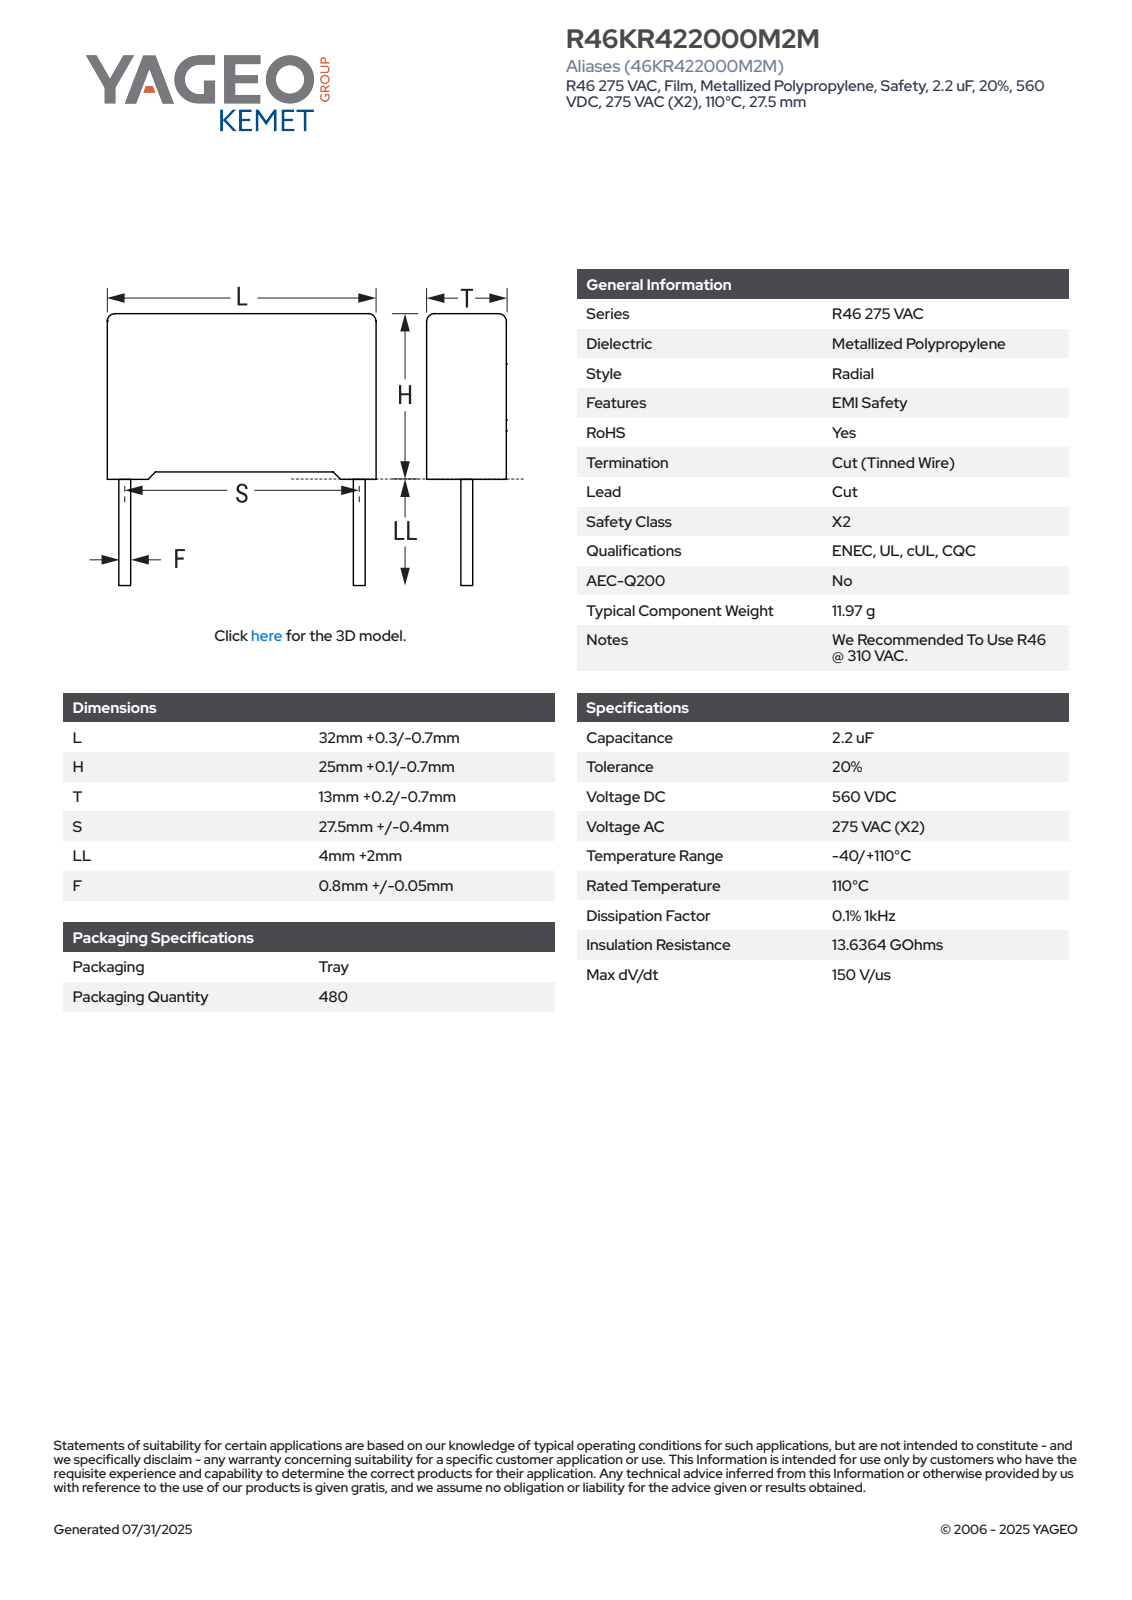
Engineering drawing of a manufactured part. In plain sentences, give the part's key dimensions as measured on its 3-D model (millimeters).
The part is named "CFR_RB2_32X25X13_L32.3H25.1T13.2S27.5LL6F0.85". Its 3-D file was written by "SolidWorks 2021 (AUTOMOTIVE_DESIGN)". It is 4 solids with 85 faces: 77 planar, 8 cylindrical and 0 other. Overall it measures 32.3 by 31.1 by 13.21 millimeters. Its volume is 10 382 cubic millimeters and its surface area 3 219 square millimeters. Round bosses or shafts: 2 of diameter 0.85. Partial cylindrical surfaces (rounded edges, fillets, slot ends): 4 of radius 0.5. The main face-to-face distances are 13.2, 32.3, 24.23, 24.35, 0.75, 0.87, 25.1, 1.08, 13.21, 31.22.
